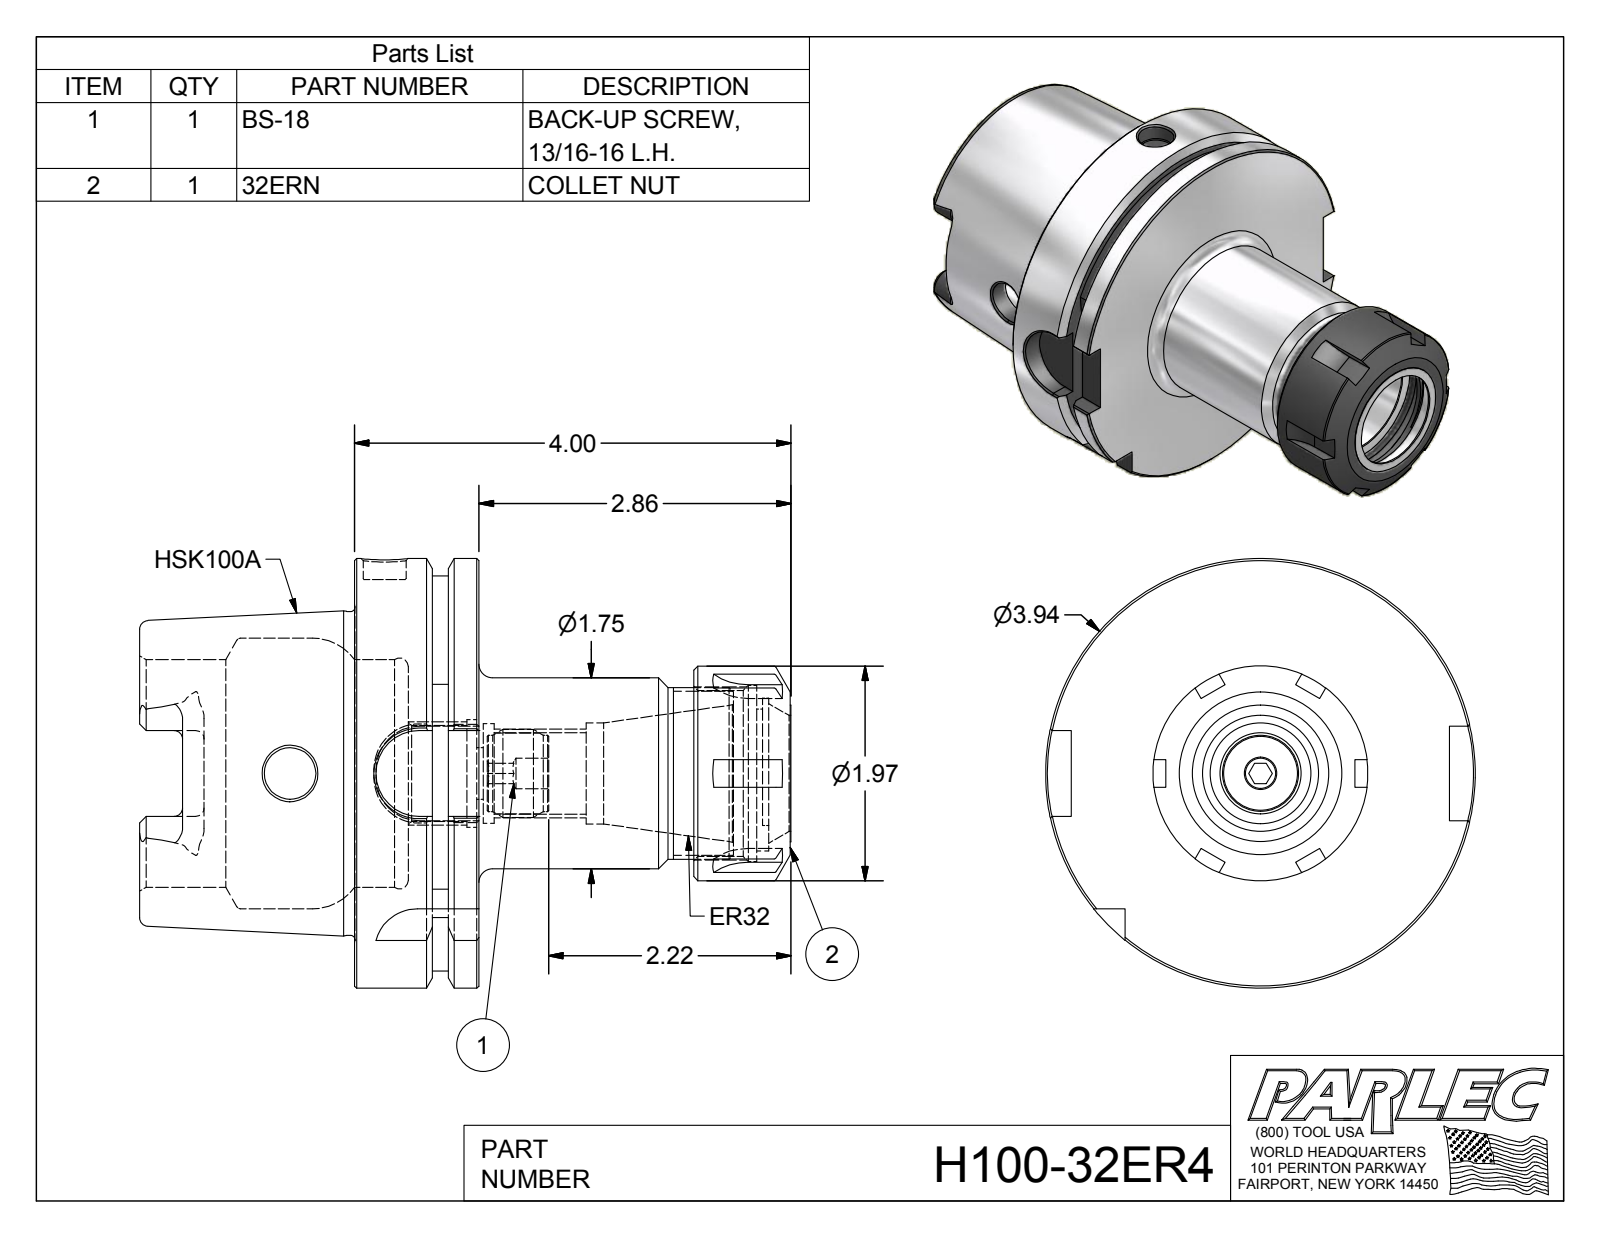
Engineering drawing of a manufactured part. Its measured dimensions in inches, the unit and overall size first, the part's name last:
Units: inches
Overall size (bounding box): 5.969 × 3.937 × 3.937
Round holes (diameter × count): ⌀0.472 ×2, ⌀0.28 ×1, ⌀0.394 ×1, ⌀0.745 ×1, ⌀0.881 ×1, ⌀0.912 ×1, ⌀0.925 ×1, ⌀0.985 ×1, ⌀1.063 ×1, ⌀1.299 ×1, ⌀1.522 ×1, ⌀1.614 ×1
Round bosses / shafts (diameter × count): ⌀3.937 ×1, ⌀2.967 ×1, ⌀1.969 ×1, ⌀1.75 ×1, ⌀1.575 ×1, ⌀1.252 ×1, ⌀0.805 ×1, ⌀0.7 ×1
Partial cylindrical surfaces — rounded edges, fillets, slot ends (radius × count): R0.079 ×6, R0.5 ×6, R0.192 ×4, R0.394 ×4, R0.689 ×1, R1.811 ×1
Main face-to-face distances: 1.142, 0.492, 0.65, 1.969, 2.461, 3.11, 2.83, 0.861, 0.369, 0.28
Hole centre spacings: 0.059
Volume: 20.44 in³ · Surface area: 112.3 in²
Bodies: 3 solids, 197 faces (77 planar, 53 cylindrical, 67 other)
Part name (STEP PRODUCT): H100-32ER4; H100-32ER4-1; BS-18; 32ERN
STEP written by: Autodesk Inventor 2012 (AUTOMOTIVE_DESIGN)
